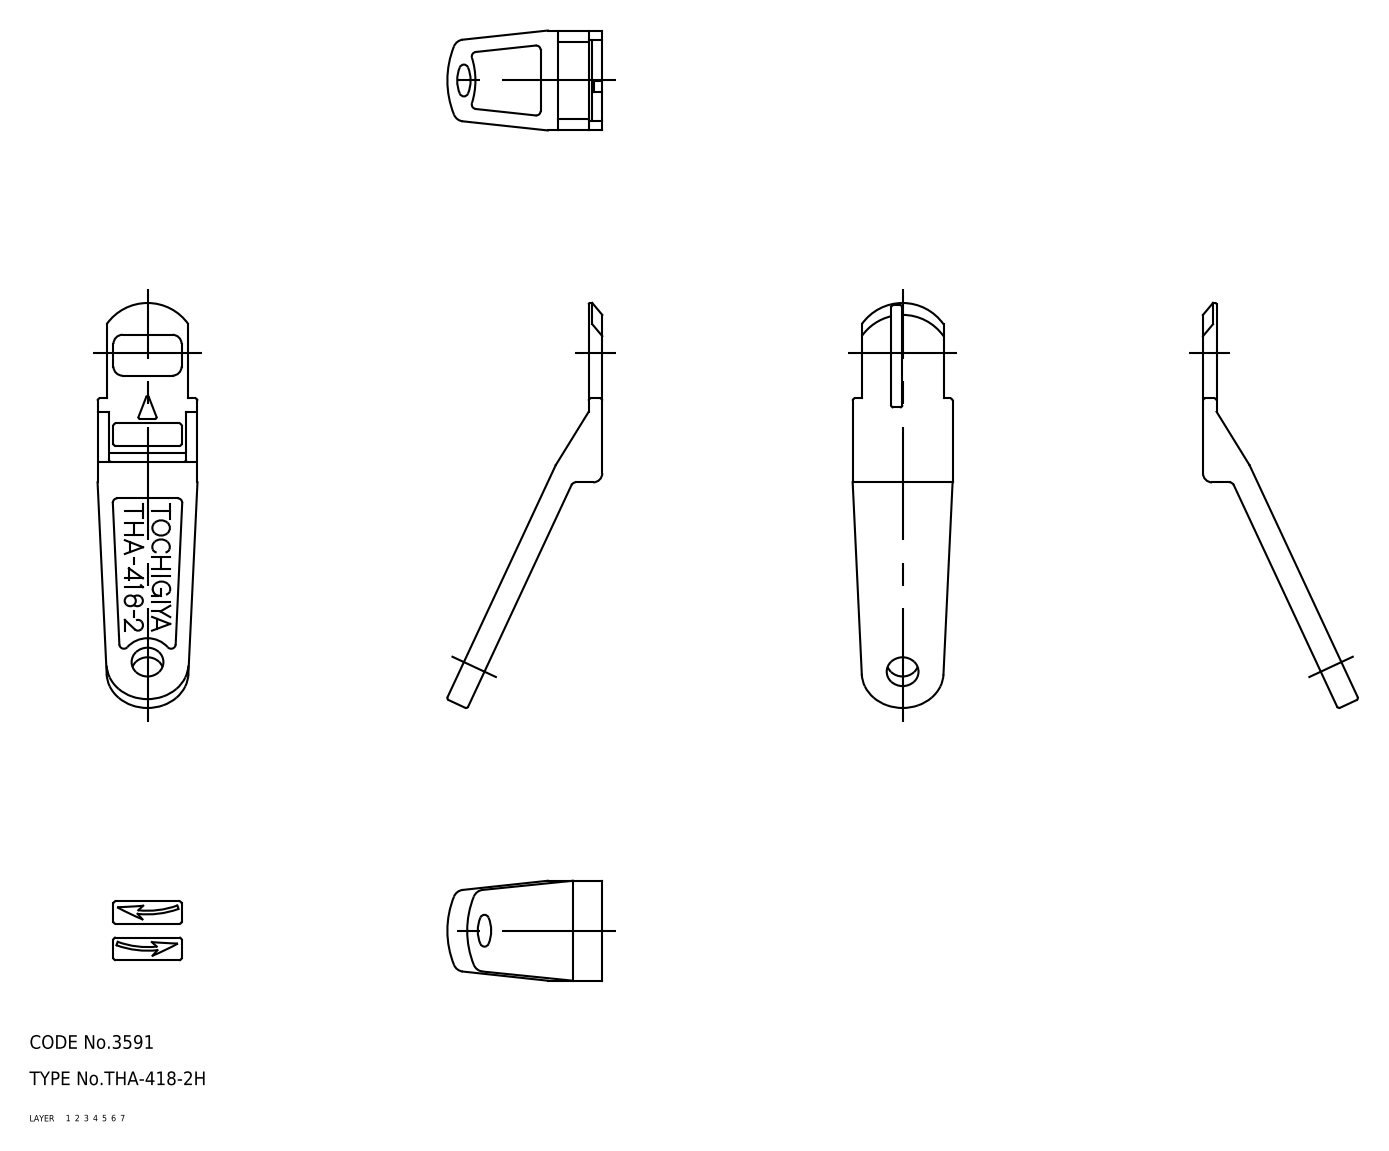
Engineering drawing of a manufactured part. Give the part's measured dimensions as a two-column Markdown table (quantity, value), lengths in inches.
| quantity | value |
| --- | --- |
| part name | key_handle |
| STEP written by | CADfix (AUTOMOTIVE_DESIGN) |
| units | inches |
| bodies | 1 solid, 72 faces (0 planar, 0 cylindrical, 72 other) |
| overall size | 3.511 × 1.343 × 0.866 |
| volume | 0.487 in³ |
| surface area | 7.549 in² |
